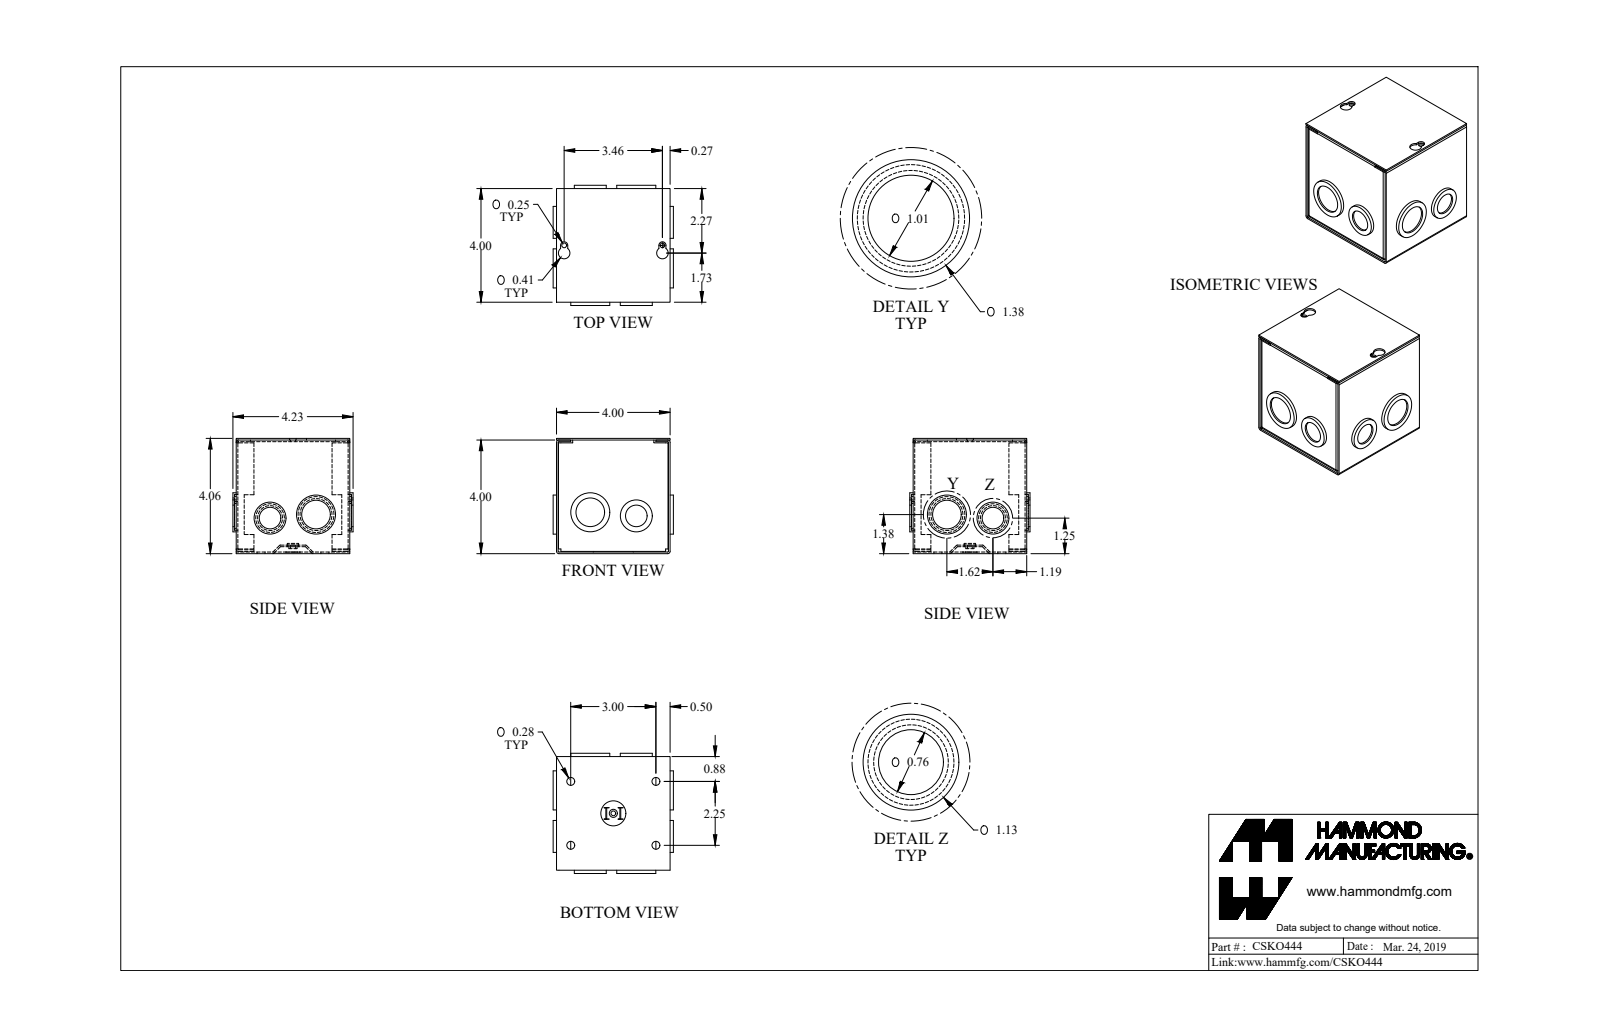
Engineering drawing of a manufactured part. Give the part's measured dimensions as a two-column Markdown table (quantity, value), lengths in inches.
| quantity | value |
| --- | --- |
| part name | CSKO444_Default |
| STEP written by | SolidWorks 2019 (CONFIG_CONTROL_DESIGN) |
| units | inches |
| bodies | 4 solids, 301 faces (169 planar, 124 cylindrical, 8 other) |
| overall size | 4.234 × 4.234 × 4.057 |
| volume | 6.5 in³ |
| surface area | 233.9 in² |
| round holes (diameter × count) | 1.011 × 6, 0.281 × 4, 0.17 × 3, 0.761 × 3, 1.261 × 3, 0.5 × 1 |
| round bosses / shafts (diameter × count) | 1.125 × 4, 1.375 × 3, 0.875 × 3, 1.125 × 2, 0.875 × 1, 0.492 × 1, 0.284 × 1 |
| partial cylindrical surfaces (radius × count) | 0.029 × 12, 0.086 × 12, 0.057 × 8, 0.125 × 2, 0.203 × 2 |
| main face-to-face distances | 0.057, 3.943, 4, 3.886, 4.057, 0.07, 3.873, 0.114, 0.127, 3.93 |
| hole center spacings | 1.148, 1.875, 3.42, 1.624, 0.125, 1.125, 1.62, 1.73 |
